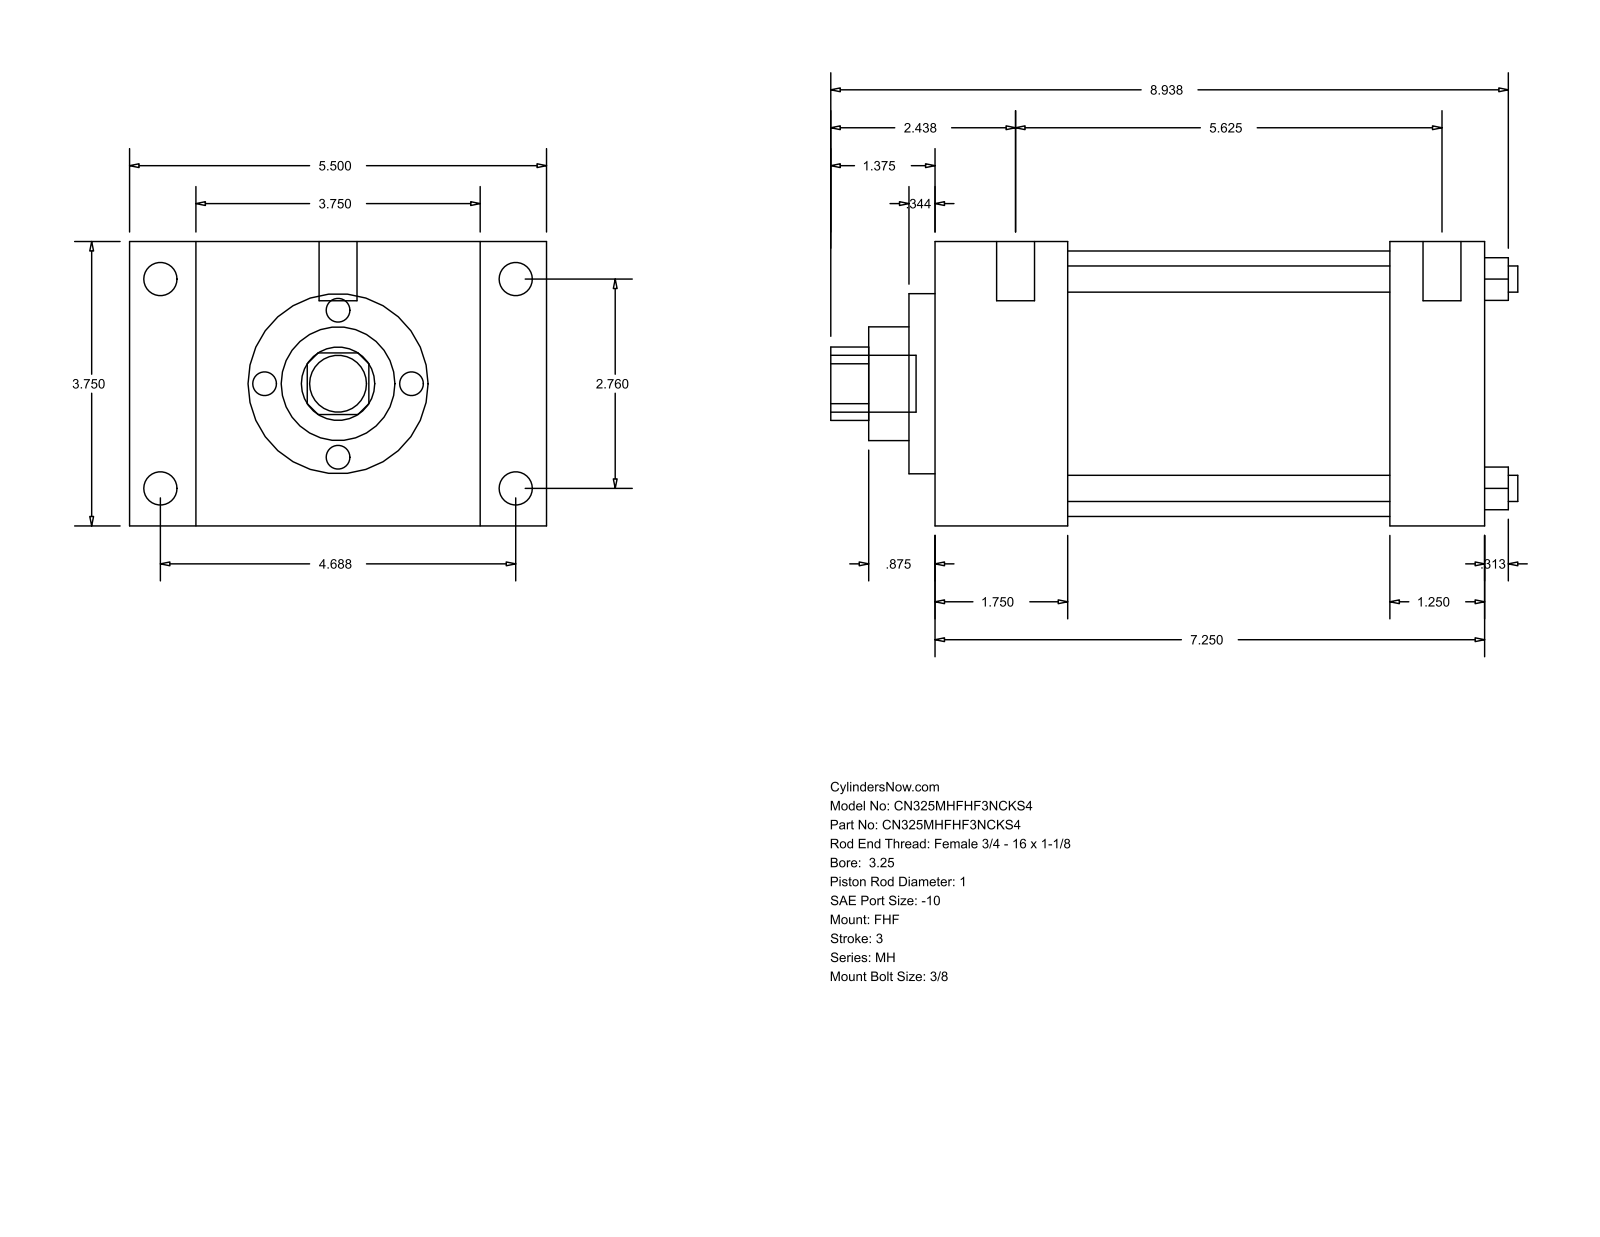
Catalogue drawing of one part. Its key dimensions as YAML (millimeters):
part_name: "MH_FHF__0325_1"
step_written_by: "GSSL Pune (CONFIG_CONTROL_DESIGN)"
units: millimeters
bodies: {solids: 0, faces: 90, planar: 61, cylindrical: 29, other: 0}
overall_size: [230.19, 139.7, 95.25]
round_holes:
  - {diameter: 8.76, count: 4}
  - {diameter: 25.4, count: 1}
  - {diameter: 38.1, count: 1}
  - {diameter: 60.33, count: 1}
  - {diameter: 88.9, count: 1}
round_bosses_or_shafts:
  - {diameter: 11.13, count: 4}
  - {diameter: 5.56, count: 4}
  - {diameter: 12.7, count: 2}
  - {diameter: 19.05, count: 1}
partial_cylinders:
  - {radius: 12.29, count: 1}
face_to_face_distances: [95.24, 184.15, 44.46, 139.69, 22.23, 117.47, 139.7, 152.4, 107.94, 31.75]
hole_center_spacings: [49.57, 70.1, 99.14]
